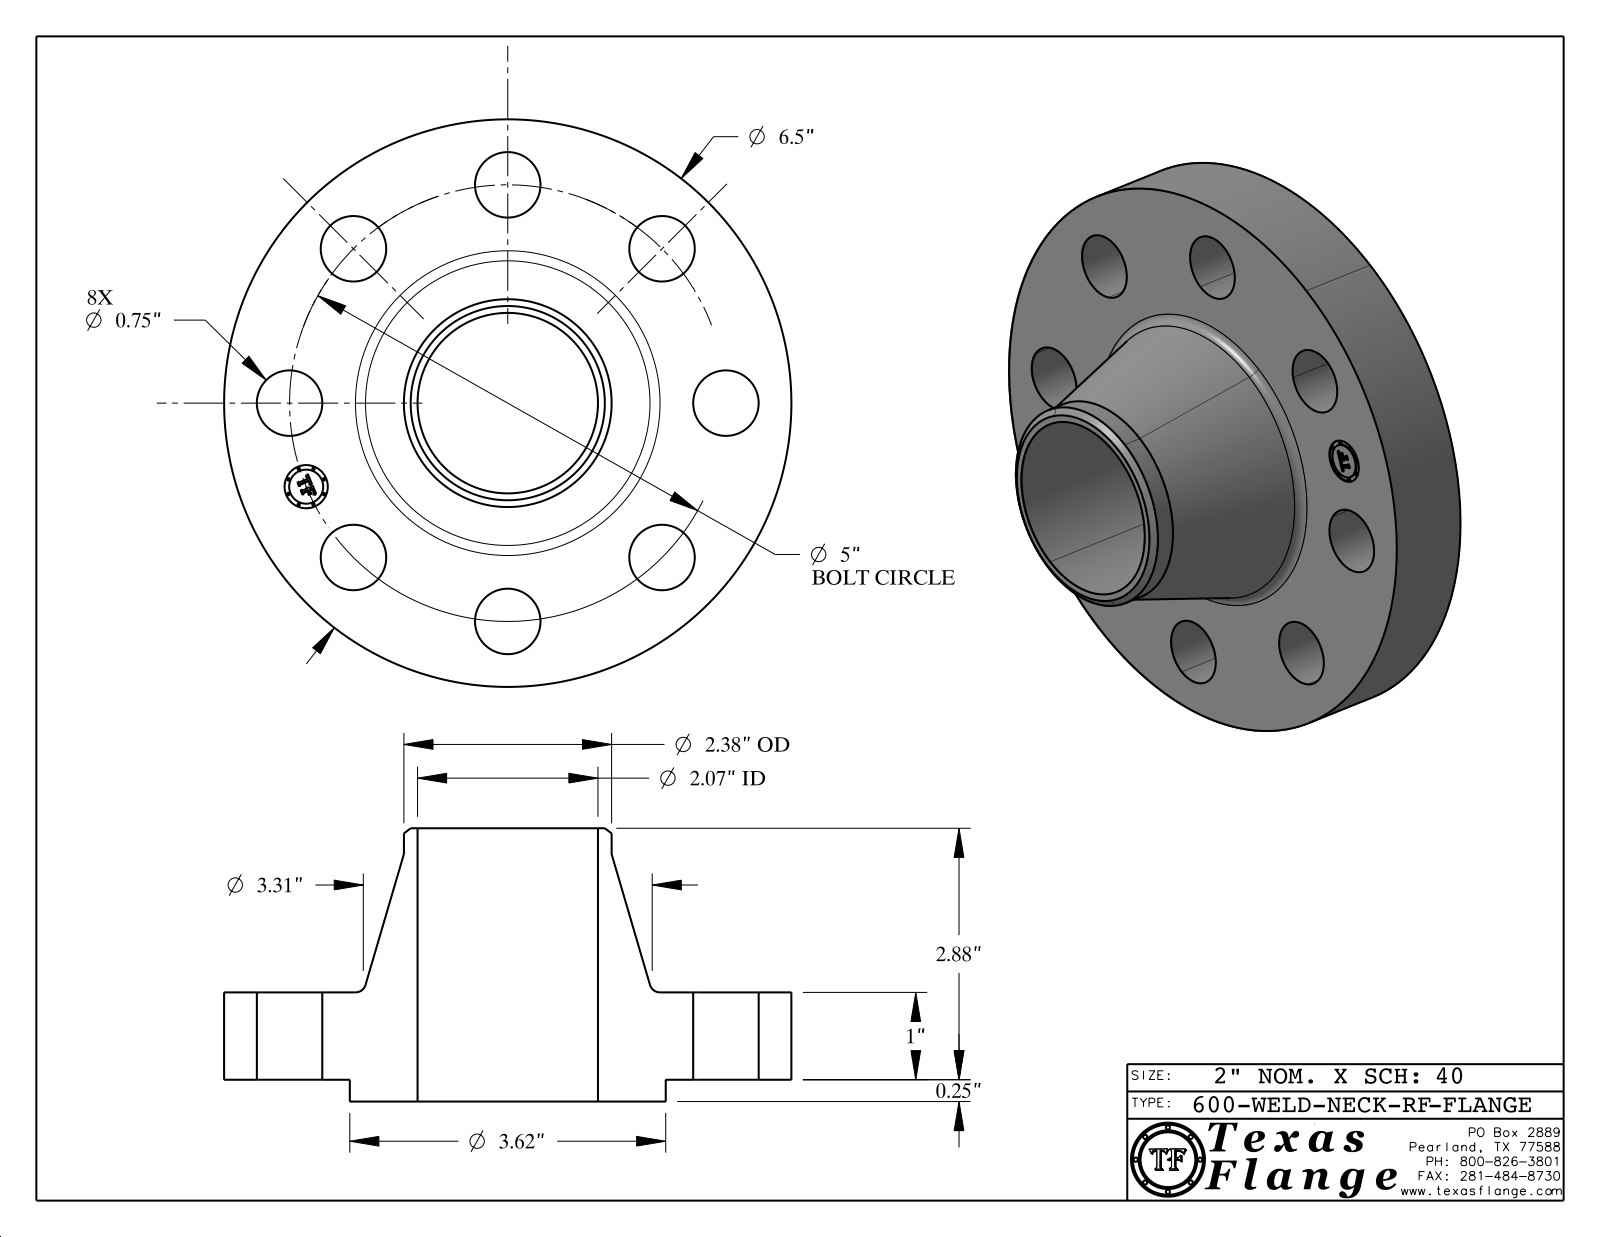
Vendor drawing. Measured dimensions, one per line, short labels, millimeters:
name: 600-WELD-NECK-RF
written by: CATIA V5 STEP AP214 (AUTOMOTIVE_DESIGN)
unit: mm
bodies: 1 solid, 419 faces (369 planar, 44 cylindrical, 6 other)
size: 165.1 × 165.1 × 79.5
volume: 543 900 mm³; area: 82 190 mm²
holes: 8× ⌀19.1, 1× ⌀12.6, 1× ⌀52.5
bosses: 8× ⌀0.8, 1× ⌀165.1, 1× ⌀91.9, 1× ⌀60.5, 1× ⌀9.9
face distances: 25.4, 6.4, 31.8, 79.5, 73.2, 47.8, 31.4, 25, 0.4, 48.1
hole spacings: 63.5, 48.6, 89.8, 117.3, 127, 24.8, 70.6, 105.6
